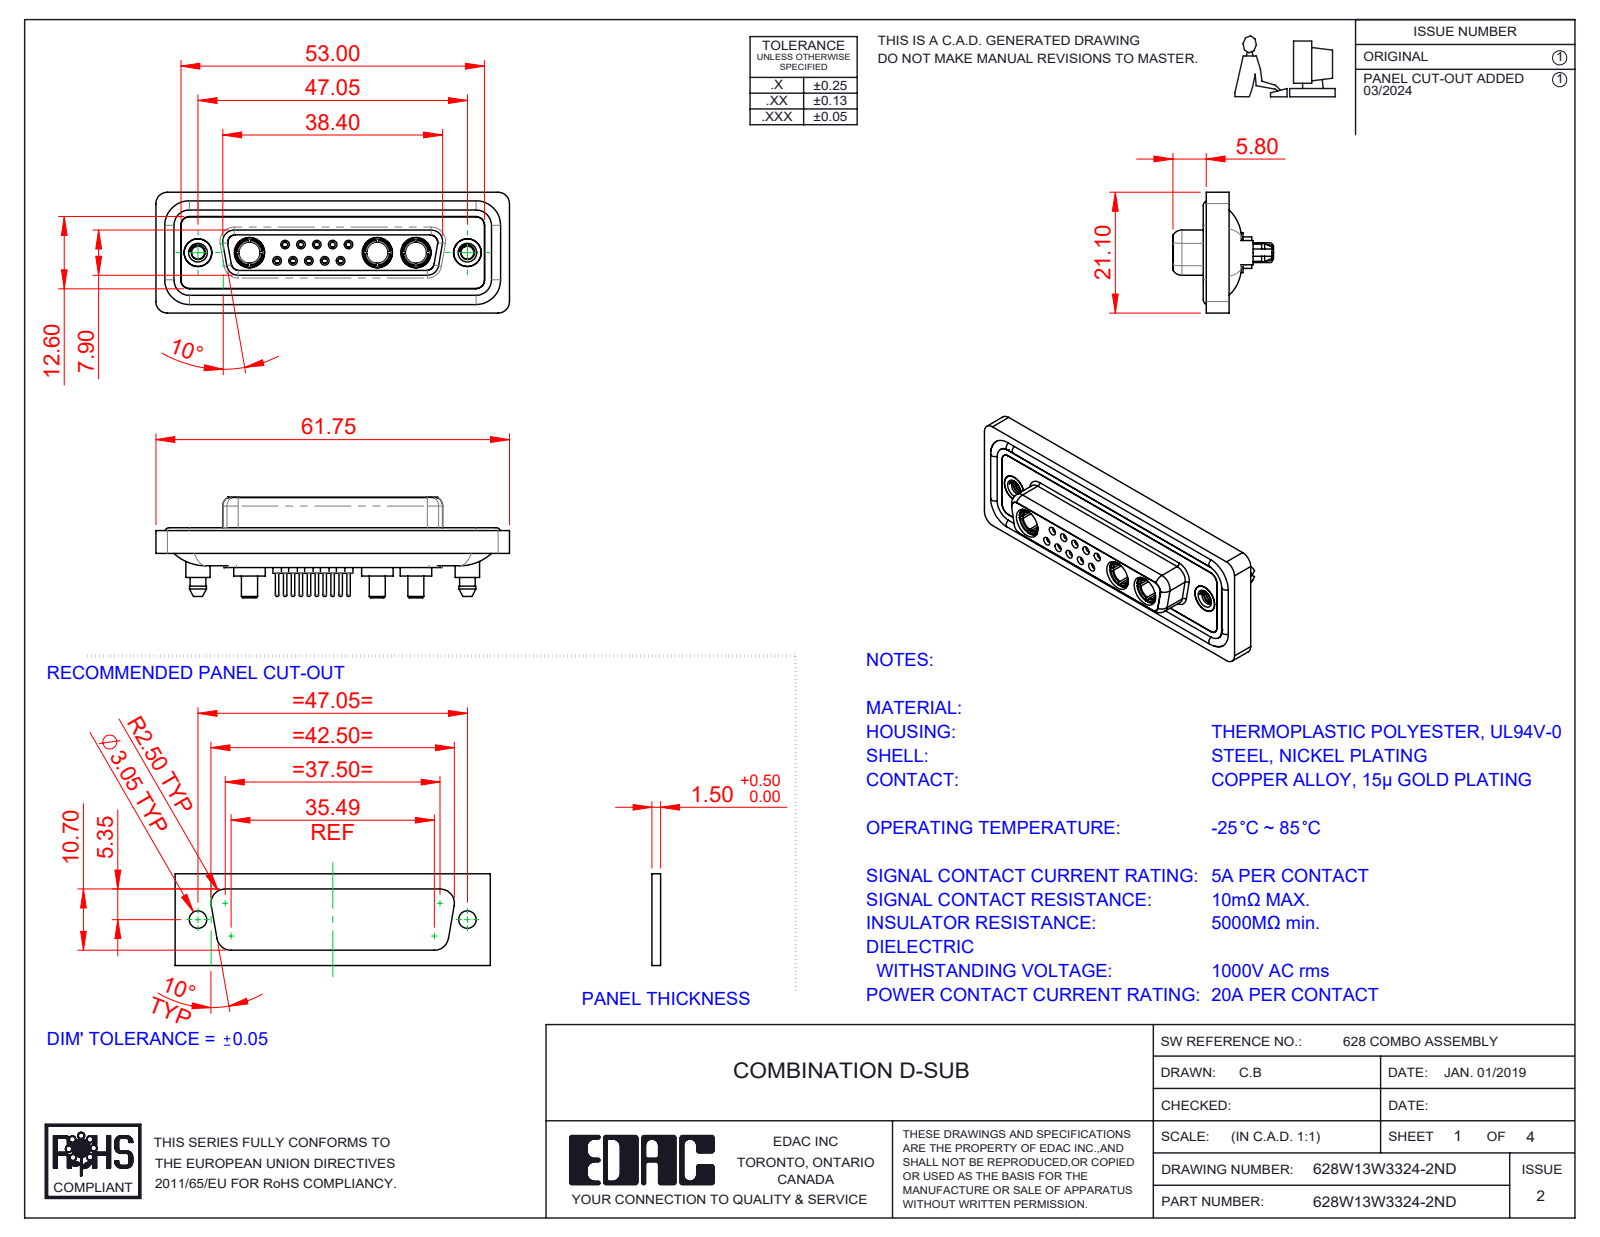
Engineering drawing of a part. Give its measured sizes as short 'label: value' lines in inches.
name: 628Combo Shell Front_25 Contacts; 628W13W3324-2ND; 628Combo Threaded Boardlock_D; 628Combo Contact Row 2_24 (+5 more)
written by: SolidWorks 2023 (CONFIG_CONTROL_DESIGN)
unit: in
bodies: 23 solids, 1224 faces (358 planar, 495 cylindrical, 371 other)
size: 2.431 × 0.831 × 0.691
volume: 0.513 in³; area: 21.77 in²
holes: 10× ⌀0.035, 10× ⌀0.043, 10× ⌀0.059, 10× ⌀0.079, 5× ⌀0.063, 5× ⌀0.067, 5× ⌀0.191, 3× ⌀0.146, 3× ⌀0.209, 2× ⌀0.089, 2× ⌀0.157, 2× ⌀0.159
bosses: 10× ⌀0.087, 10× ⌀0.024, 9× ⌀0.063, 3× ⌀0.217, 3× ⌀0.205, 3× ⌀0.195, 3× ⌀0.187, 3× ⌀0.148
rounds: 24× R0.059, 18× R0.079, 10× R0.063, 8× R0.053, 4× R0.01, 4× R0.02, 4× R0.024, 4× R0.026
face distances: 0.016, 0.071, 0.293, 0.222, 0.02, 0.26, 0.278, 0.063, 0.114, 0.043
hole spacings: 0.124, 0.109, 0.198, 0.198, 0.218, 0.327, 0.295, 0.109
